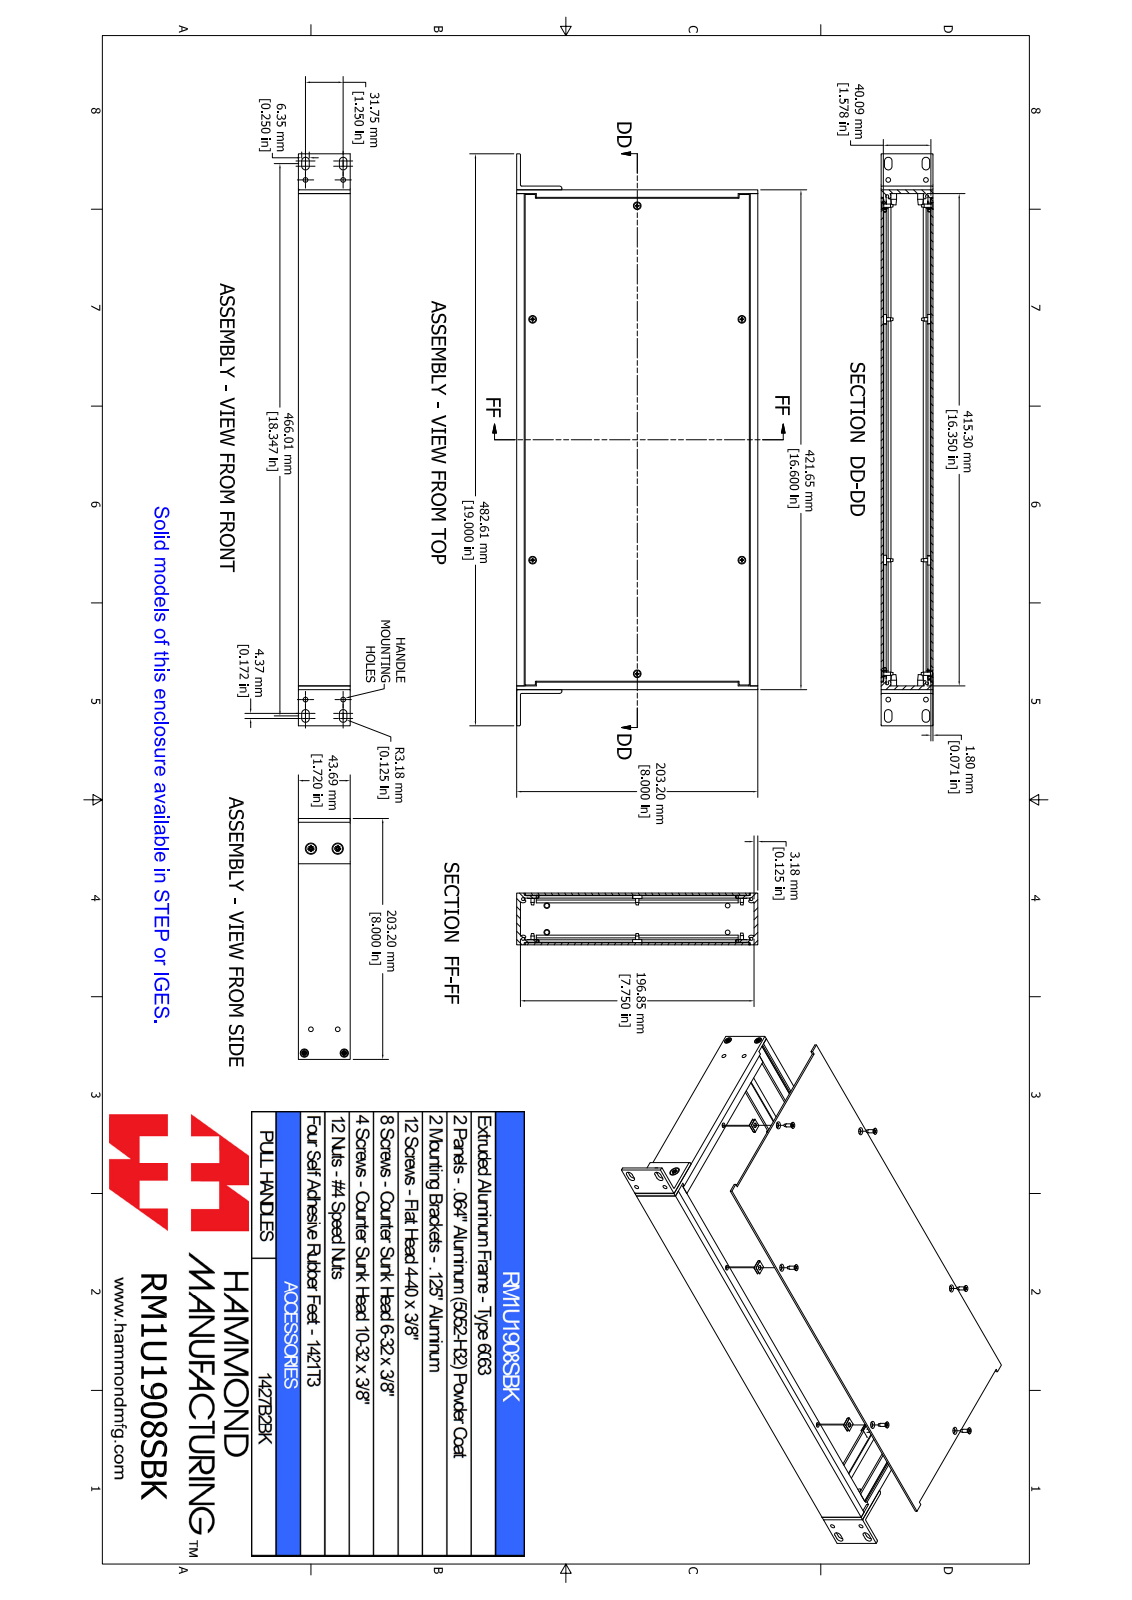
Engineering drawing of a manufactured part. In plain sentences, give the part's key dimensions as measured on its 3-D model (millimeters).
The part is named "RM1U1908SBK". Its 3-D file was written by "SolidWorks 2021 (AUTOMOTIVE_DESIGN)". It is 44 solids with 1184 faces: 564 planar, 188 cylindrical and 432 other. Overall it measures 482.6 by 203.2 by 43.7 millimeters. Its volume is 571 100 cubic millimeters and its surface area 530 900 square millimeters. Round holes: 6 of diameter 2.5, 6 of diameter 4, 6 of diameter 4.3, 4 of diameter 3.5, 4 of diameter 4, 4 of diameter 4, 2 of diameter 5.5. Round bosses or shafts: 6 of diameter 5.4, 6 of diameter 2.8, 4 of diameter 6, 4 of diameter 3.5, 2 of diameter 8.5, 2 of diameter 4.8. Partial cylindrical surfaces (rounded edges, fillets, slot ends): 18 of radius 1, 16 of radius 3.2, 12 of radius 1.2, 8 of radius 1.3, 6 of radius 1, 4 of radius 0.9, 2 of radius 2. The main face-to-face distances are 1.8, 41.9, 43.7, 40.1, 37.6, 3.2, 4.2, 39.4, 2.4, 3.2. The hole center spacings are 172.6, 20.8, 152.4, 174.8, 20.8, 22.6, 31.8, 33.6.
